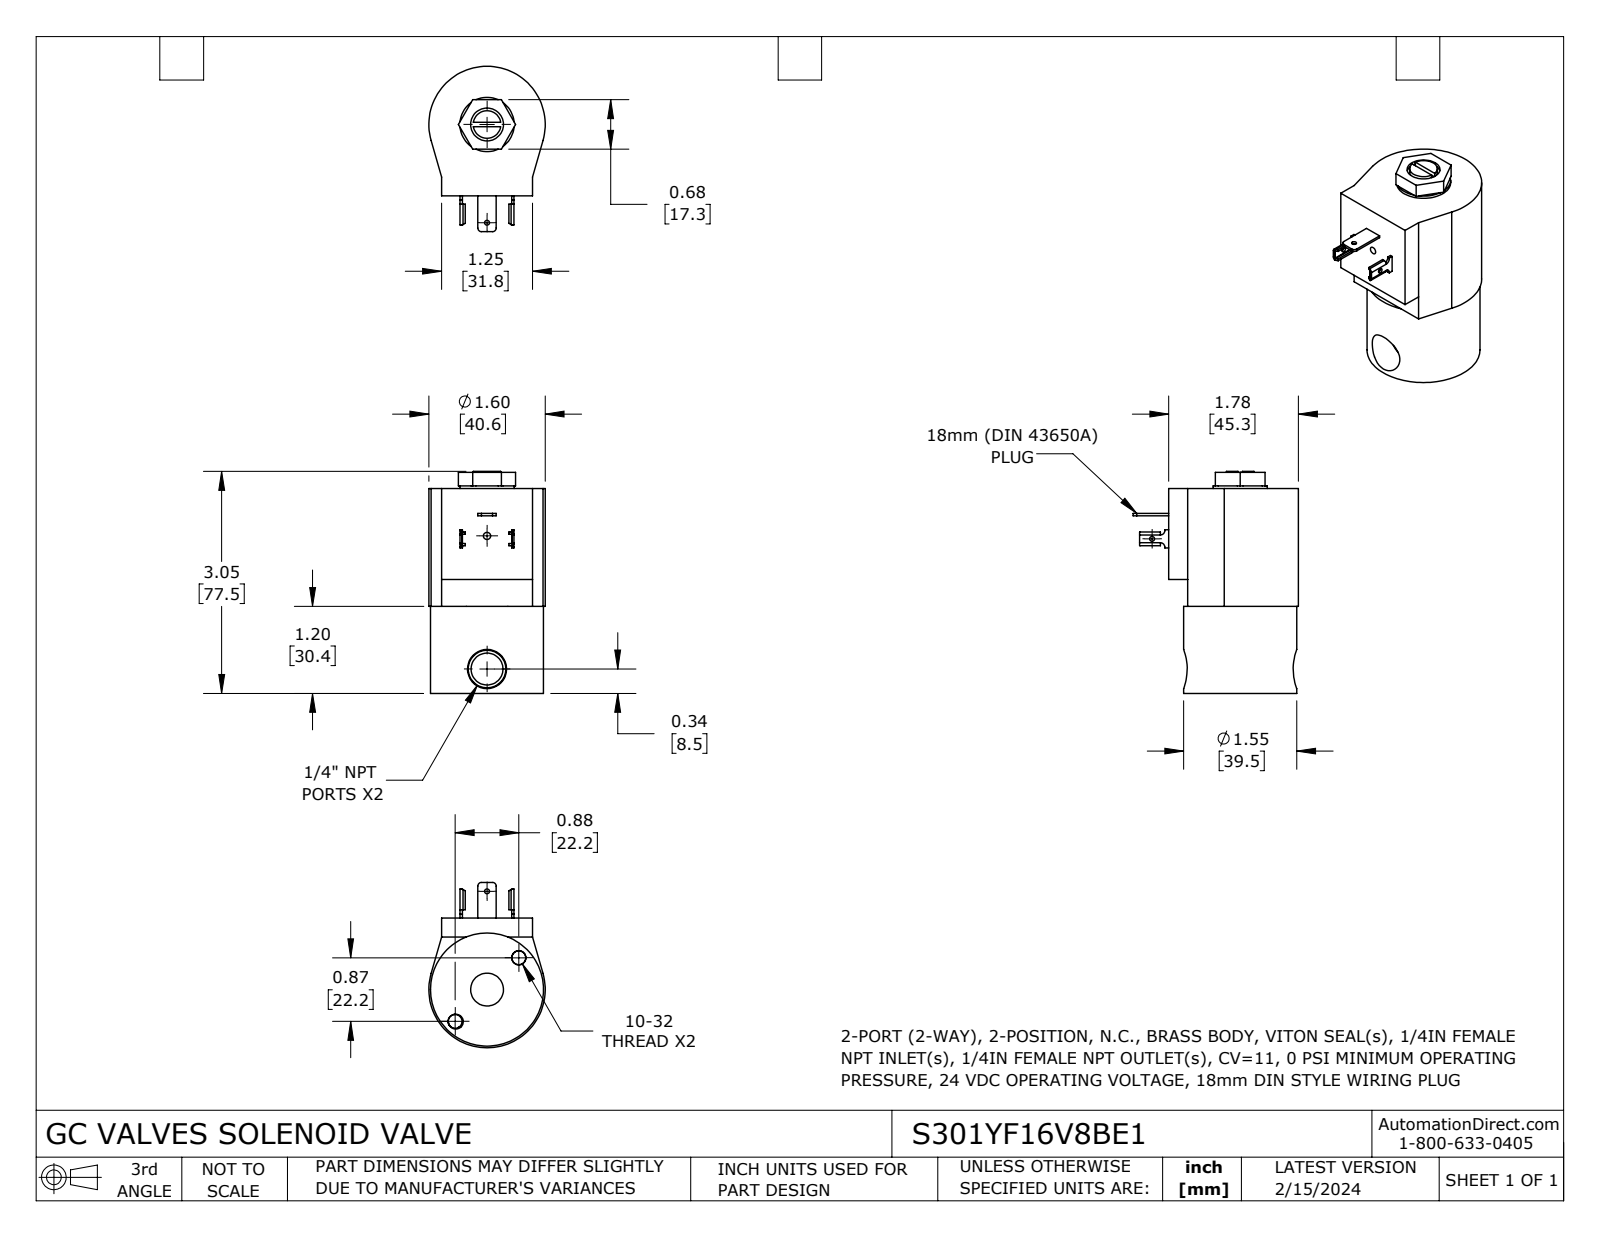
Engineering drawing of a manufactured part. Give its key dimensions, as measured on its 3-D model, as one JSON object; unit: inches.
{"part_name": "S301YF16V8BE1", "step_written_by": "SolidWorks 2023 (CONFIG_CONTROL_DESIGN)", "units": "inches", "bodies": {"solids": 2, "faces": 171, "planar": 78, "cylindrical": 71, "other": 22}, "overall_size": [3.061, 2.273, 1.6], "volume_in3": 5.834, "surface_area_in2": 27.56, "round_holes": [[0.19, 2], [0.066, 1], [0.067, 1], [0.1, 1], [0.438, 1], [0.451, 1]], "round_bosses_or_shafts": [[1.553, 1], [0.746, 1], [0.38, 1]], "partial_cylinders_radius": [[0.006, 4], [0.041, 4], [0.05, 2], [0.06, 2], [0.8, 1]], "face_to_face_distances": [1.62, 1.195, 2.815, 0.26, 1.565, 0.37, 1.25, 1.25, 3.038, 1.843], "hole_center_spacings": [0.618, 0.619, 1.012, 1.237, 1.35, 1.83, 1.84]}
